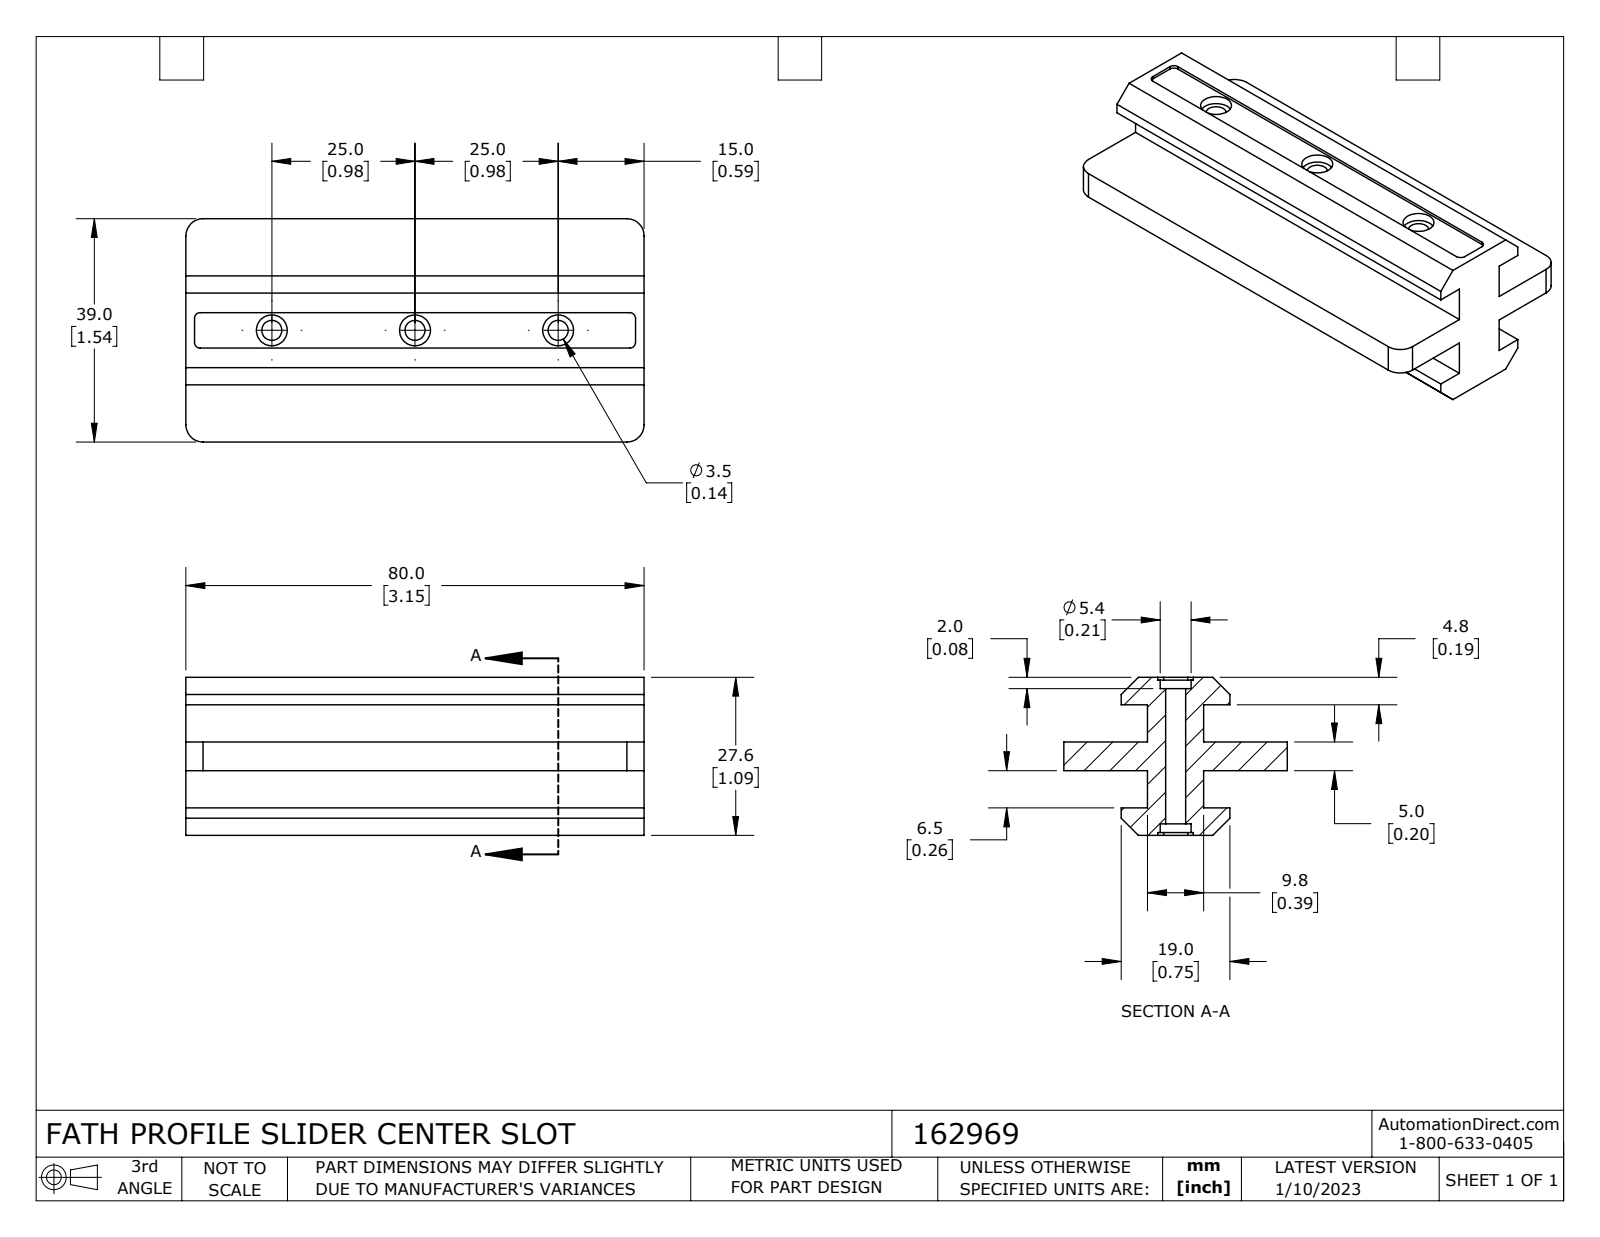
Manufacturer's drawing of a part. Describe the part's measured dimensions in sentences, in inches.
The part is named "162969". Its 3-D file was written by "SolidWorks 2021 (CONFIG_CONTROL_DESIGN)". It is 1 solid with 72 faces: 42 planar, 30 cylindrical and 0 other. Overall it measures 3.15 by 1.535 by 1.087 inches. Its volume is 2.291 cubic inches and its surface area 23.26 square inches. Round holes: 3 of diameter 0.138, 3 of diameter 0.213. Partial cylindrical surfaces (rounded edges, fillets, slot ends): 4 of radius 0.039, 4 of radius 0.118. The main face-to-face distances are 0.197, 0.256, 0.453, 0.189, 0.445, 0.642, 0.898, 0.386, 0.02, 1.067. The hole center spacings are 0.984, 1.969.
